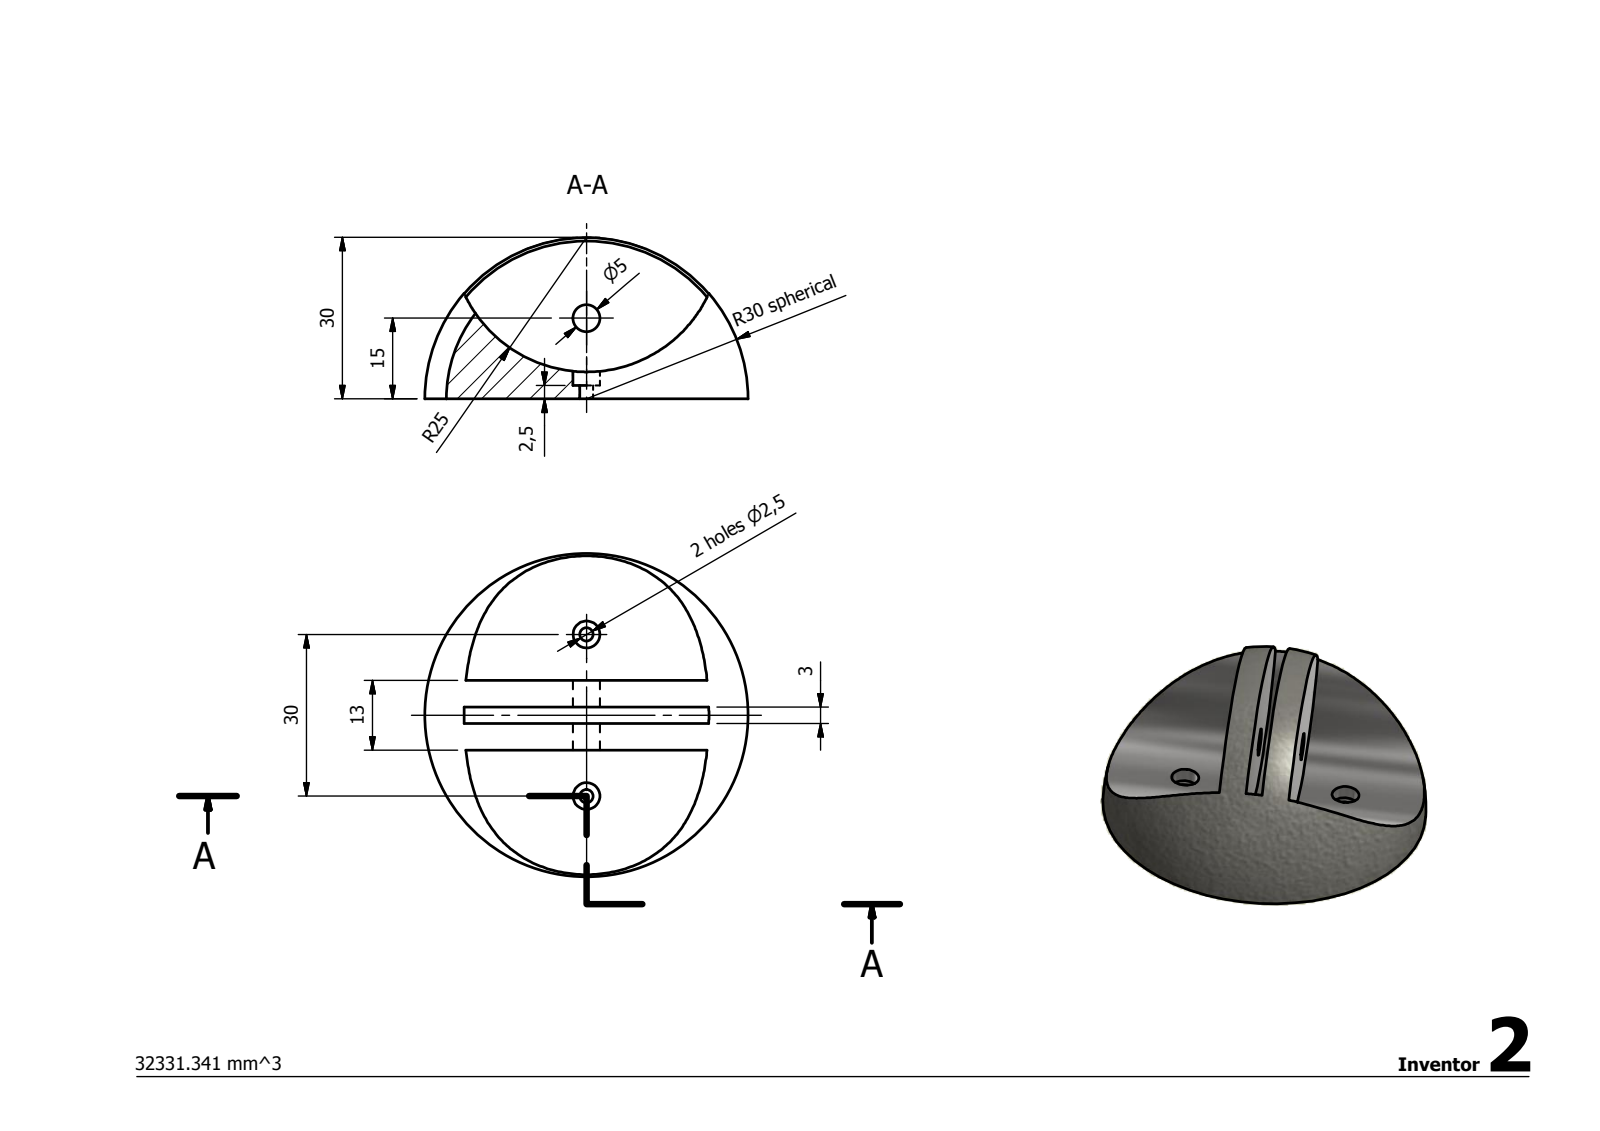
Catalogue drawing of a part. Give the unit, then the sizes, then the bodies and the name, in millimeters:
Units: millimetres
Overall size (bounding box): 60 × 60 × 29.96
Round holes (diameter × count): ⌀5 ×3, ⌀2.5 ×2
Partial cylindrical surfaces — rounded edges, fillets, slot ends (radius × count): R25 ×1
Main face-to-face distances: 5, 8, 3, 13, 2.5
Hole centre spacings: 30
Volume: 32 330 mm³ · Surface area: 11 153 mm²
Bodies: 1 solid, 17 faces (7 planar, 9 cylindrical, 1 other)
STEP written by: Autodesk Inventor 2014 (AUTOMOTIVE_DESIGN)
